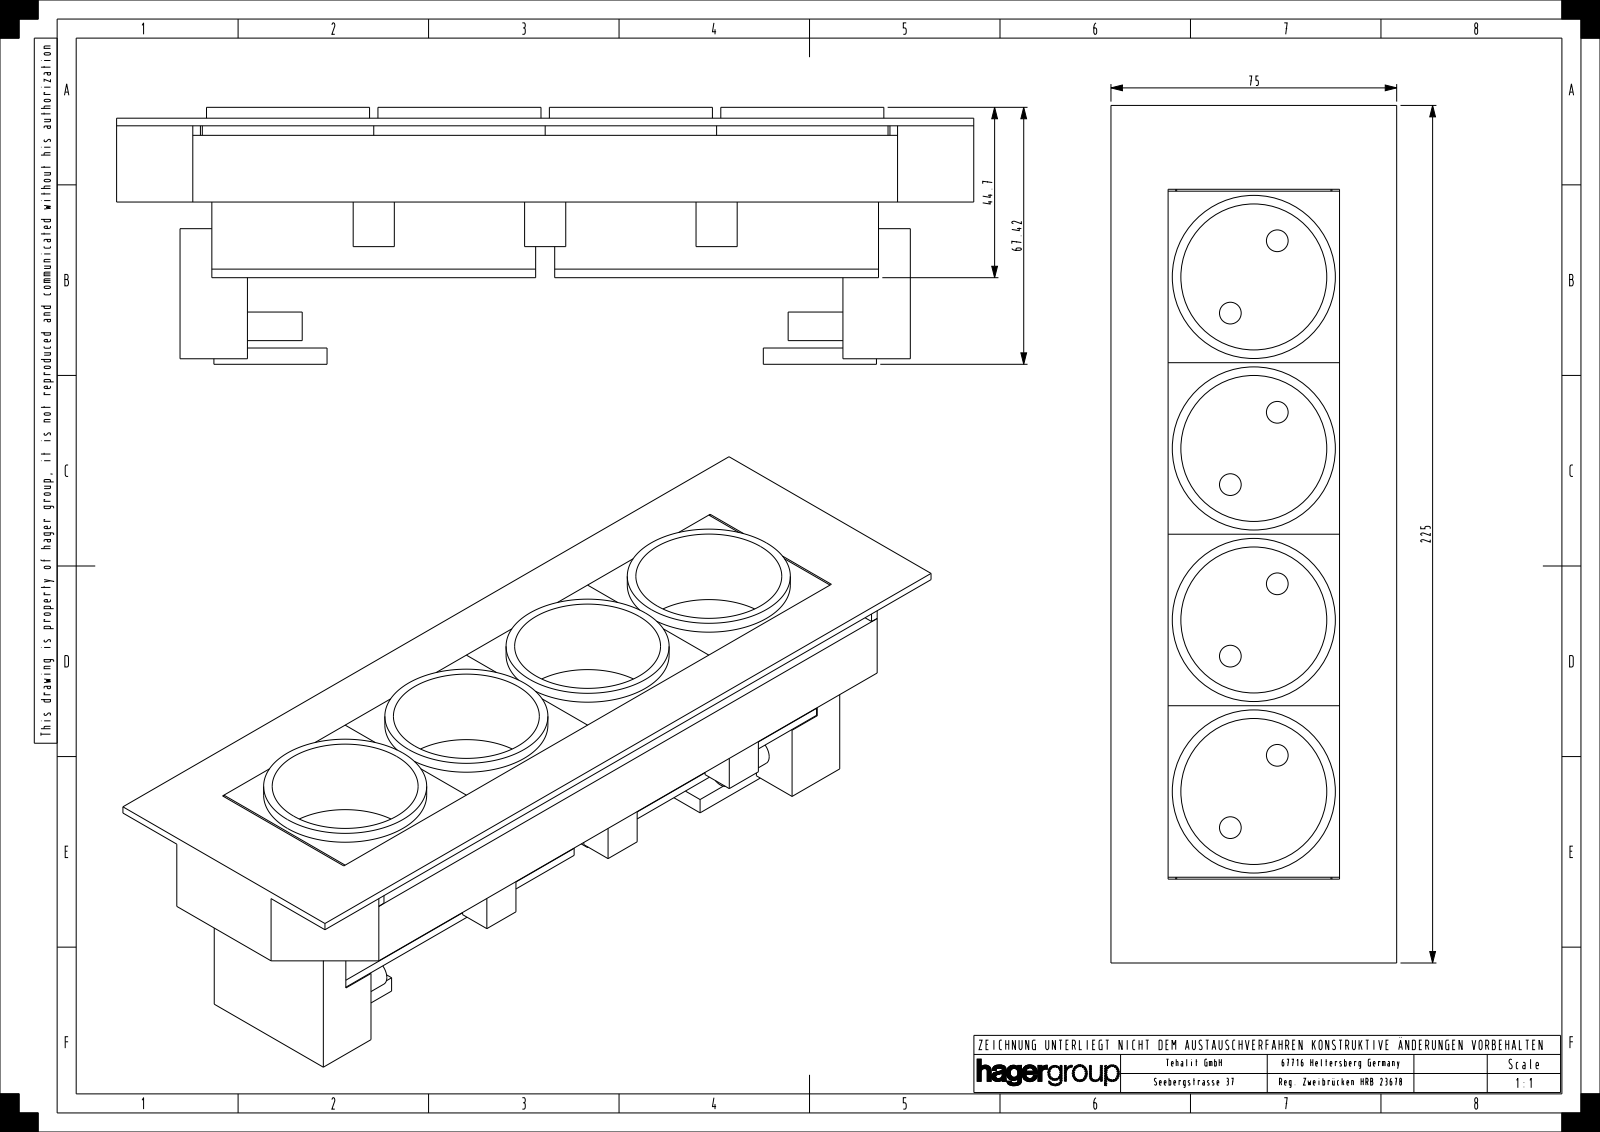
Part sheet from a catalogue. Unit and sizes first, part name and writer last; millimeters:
Units: millimetres
Overall size (bounding box): 225 × 75 × 67.42
Round holes (diameter × count): ⌀5.7 ×8, ⌀38.3 ×4
Round bosses / shafts (diameter × count): ⌀42.8 ×4, ⌀38.5 ×4, ⌀7.5 ×3
Main face-to-face distances: 0.8, 2.5, 17.5, 2, 17, 4.5, 39.2, 42.5, 41.7, 41.85
Hole centre spacings: 45, 11.31, 36.04, 54.84, 90, 22.63, 80.75, 99.68
Volume: 291 313 mm³ · Surface area: 151 932 mm²
Bodies: 9 solids, 221 faces (169 planar, 52 cylindrical, 0 other)
Part name (STEP PRODUCT): GTVR400_1; SOCKEL-2-FACH-VEREINFACHT_8; ABDECKUNG-SIMPLIFIED_9; ESR2339010-VEREINFACHT_ASM_7_AF2_ASM (+6 more)
STEP written by: CREO PARAMETRIC BY PTC INC, 2022281 (AUTOMOTIVE_DESIGN)
